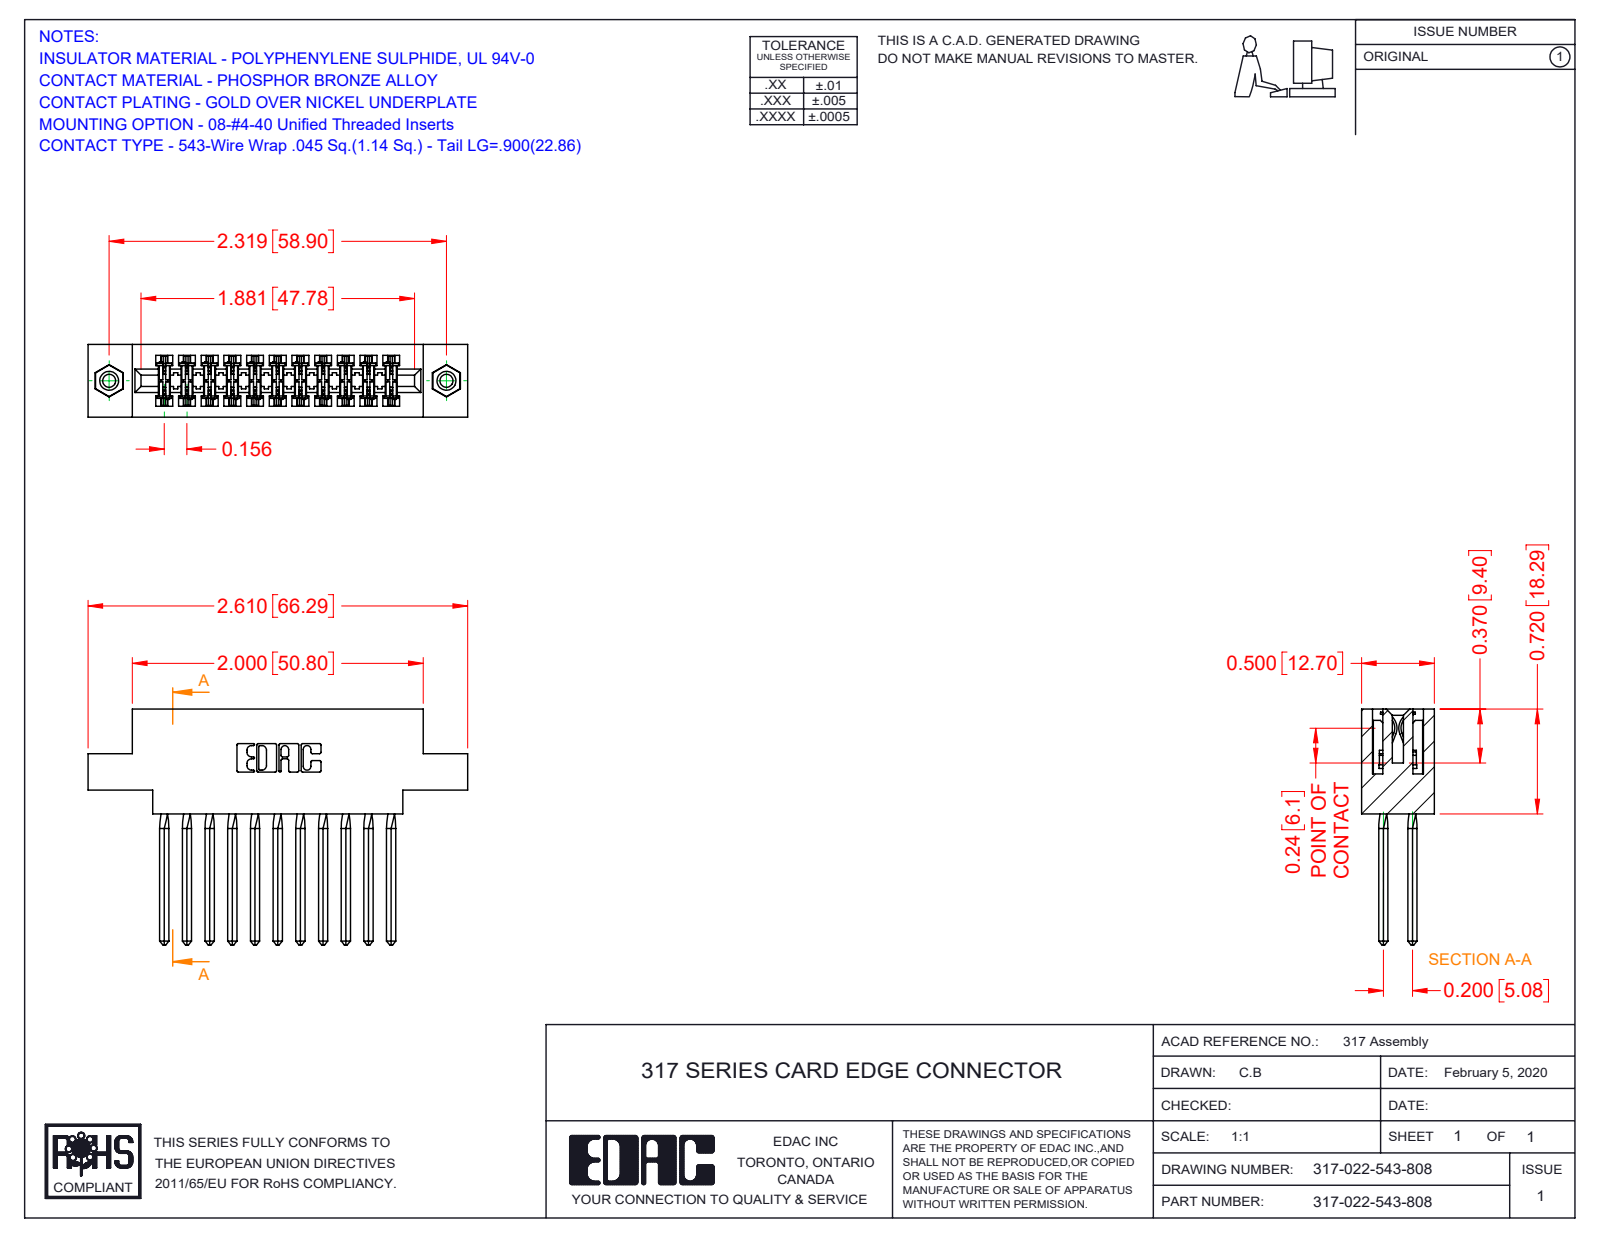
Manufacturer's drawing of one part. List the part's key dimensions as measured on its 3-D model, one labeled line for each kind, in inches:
Part name (STEP PRODUCT): 317-290-001_543; 317 Part_.156 Dia - TI; 345-250-001_345-250-003-102; 317-022-543-878
STEP written by: SolidWorks 2016 (CONFIG_CONTROL_DESIGN)
Units: inches
Bodies: 25 solids, 2120 faces (1696 planar, 320 cylindrical, 104 other)
Overall size (bounding box): 2.61 × 1.62 × 0.5
Volume: 0.621 in³ · Surface area: 22.09 in²
Round holes (diameter × count): ⌀0.089 ×2, ⌀0.125 ×2, ⌀0.156 ×2
Round bosses / shafts (diameter × count): ⌀0.155 ×2
Partial cylindrical surfaces — rounded edges, fillets, slot ends (radius × count): R0.015 ×44, R0.01 ×22, R0.007 ×6, R0.031 ×6, R0.026 ×3, R0.095 ×2, R0.1 ×2, R0.11 ×2
Main face-to-face distances: 0.5, 0.075, 0.11, 0.425, 0.22, 0.331, 0.35, 0.116, 0.156, 0.136
Hole centre spacings: 2.319
